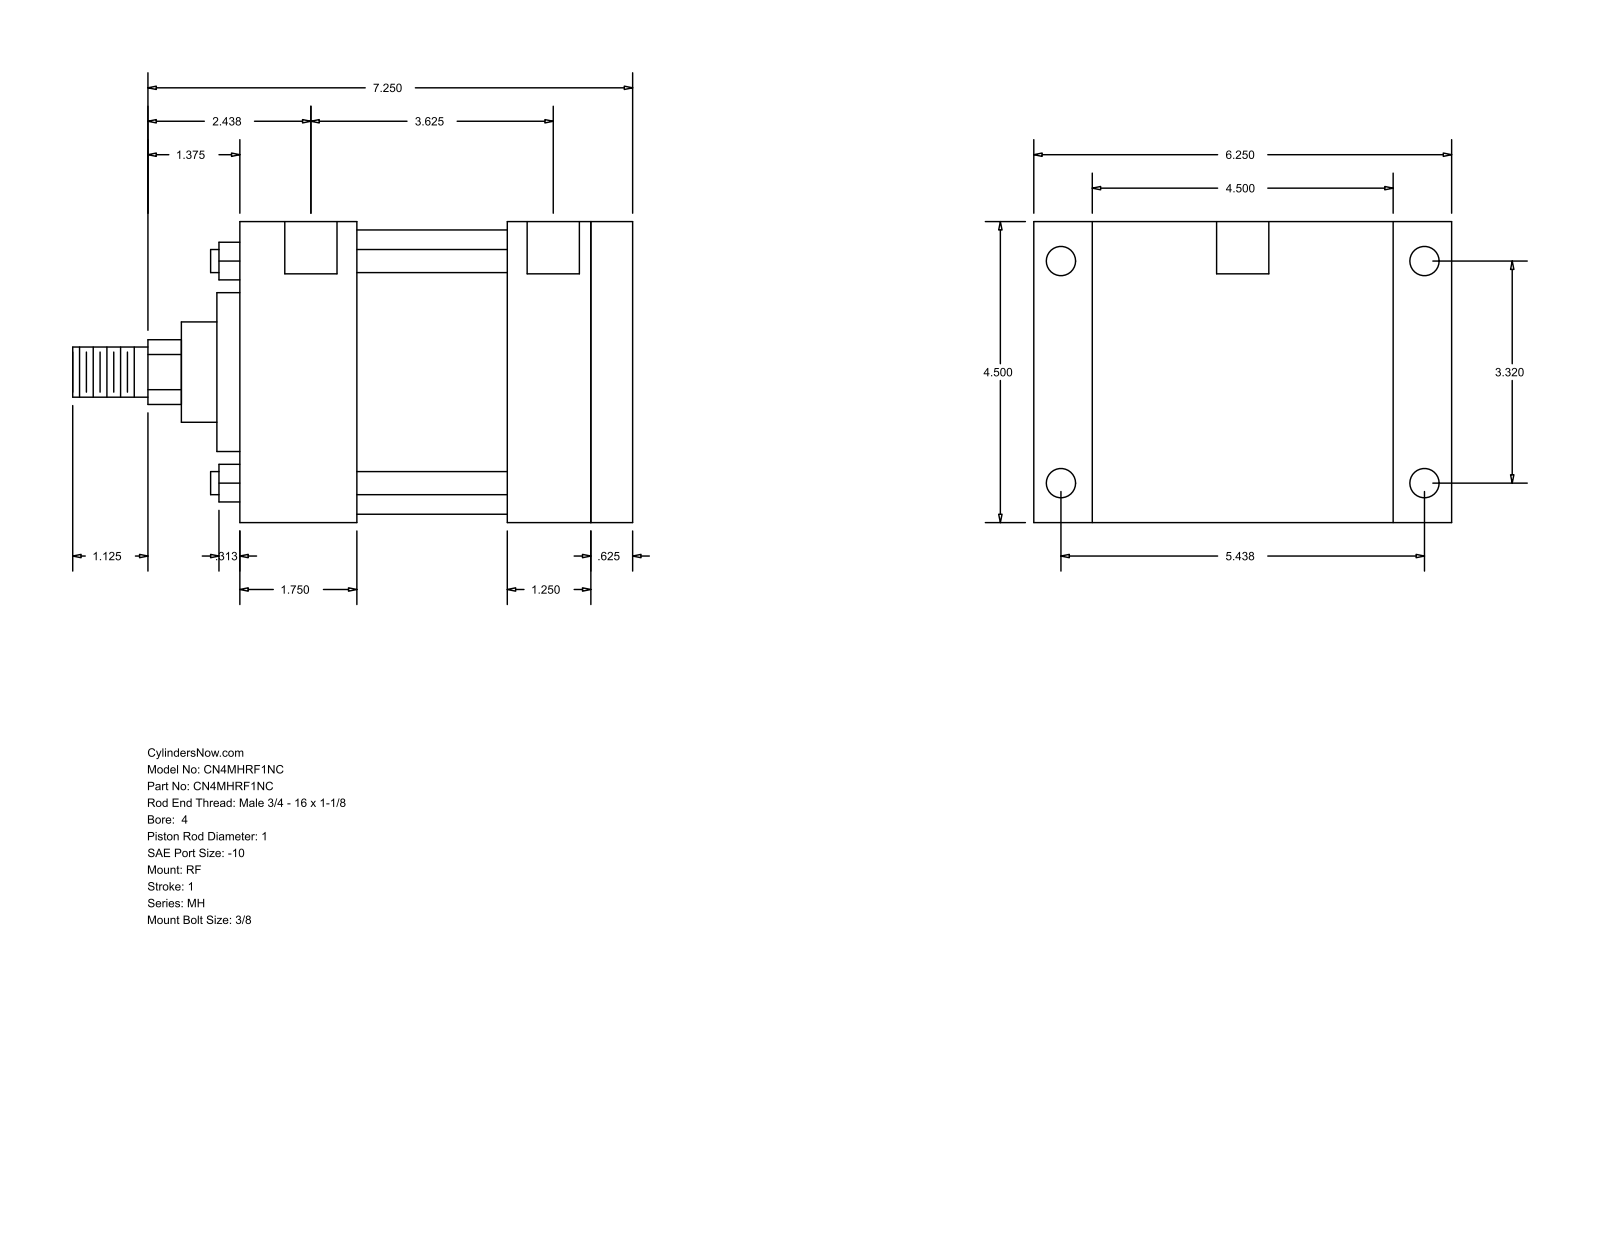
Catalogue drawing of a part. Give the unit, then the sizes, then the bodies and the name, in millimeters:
Units: millimetres
Overall size (bounding box): 212.72 × 158.75 × 114.3
Round holes (diameter × count): ⌀8.73 ×4, ⌀11.13 ×4, ⌀19.84 ×2
Round bosses / shafts (diameter × count): ⌀8.76 ×4, ⌀107.95 ×1, ⌀60.33 ×1, ⌀38.1 ×1, ⌀25.4 ×1, ⌀19.05 ×1
Partial cylindrical surfaces — rounded edges, fillets, slot ends (radius × count): R12.29 ×1
Main face-to-face distances: 114.3, 149.23, 133.36, 15.87, 136.53, 44.46, 88.9, 104.77, 101.61, 57.15
Hole centre spacings: 1.58, 84.32, 93.66, 95.24, 138.12, 161.82, 92.08
Bodies: 0 solids, 94 faces (65 planar, 29 cylindrical, 0 other)
Part name (STEP PRODUCT): MH_RF__0400_1
STEP written by: GSSL Pune (CONFIG_CONTROL_DESIGN)
